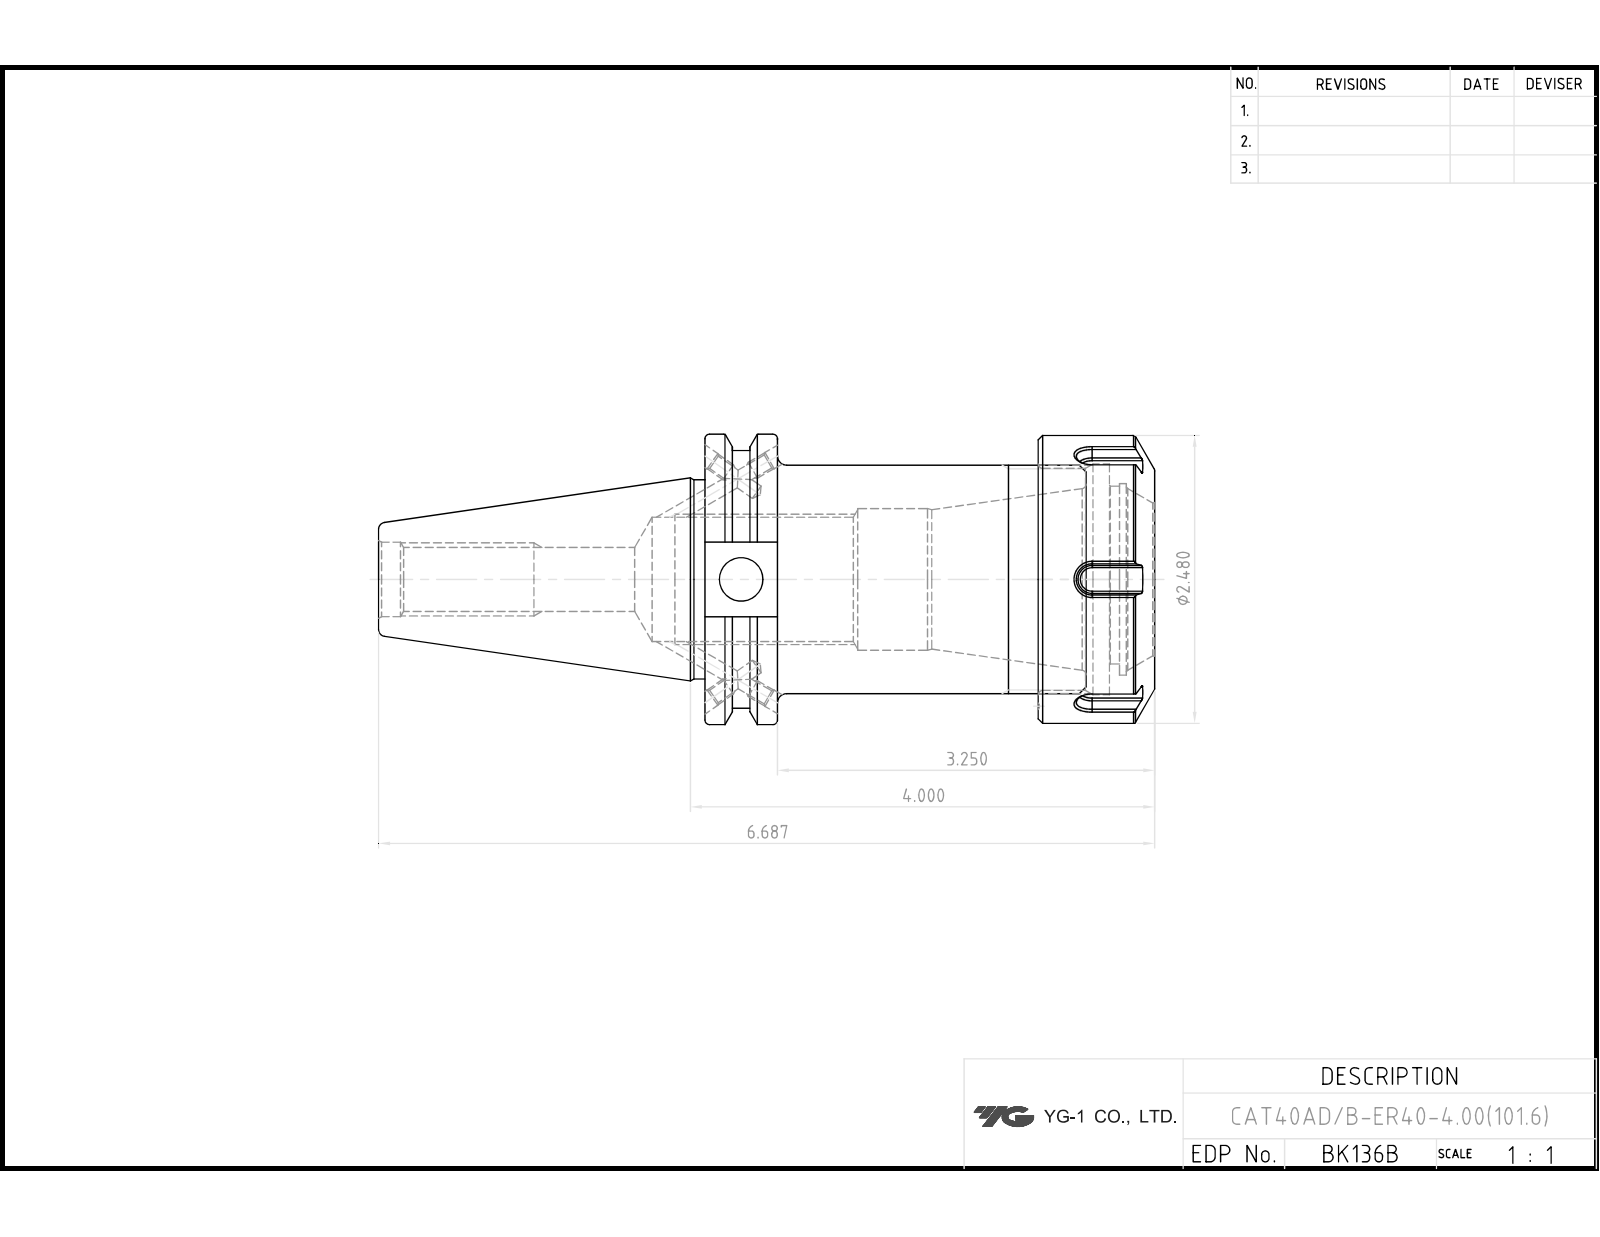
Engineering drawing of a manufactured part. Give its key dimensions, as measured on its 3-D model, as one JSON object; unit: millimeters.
{"part_name": "LO-CAT40ADB-ER40-4.00; ER40NUT", "step_written_by": "Autodesk Inventor 2024 (AUTOMOTIVE_DESIGN)", "units": "millimeters", "bodies": {"solids": 2, "faces": 169, "planar": 71, "cylindrical": 44, "other": 54}, "overall_size": [169.85, 63.5, 63], "volume_mm3": 202021, "surface_area_mm2": 51107, "round_holes": [[3.24, 4], [4, 4], [1.43, 1], [9.53, 1], [13.39, 1], [16.3, 1], [26.85, 1], [31, 1], [33.5, 1], [38.9, 1], [41.9, 1], [48.6, 1]], "round_bosses_or_shafts": [[63.5, 1], [63, 1], [56.3, 1], [50, 1], [43.6, 1]], "partial_cylinders_radius": [[0.5, 12], [8.19, 1]], "face_to_face_distances": [98.43, 72.93, 25.5, 84.93, 12, 13.5, 15.88, 57.05, 69.05, 82.55], "hole_center_spacings": [0.48, 27.55, 27.75]}
